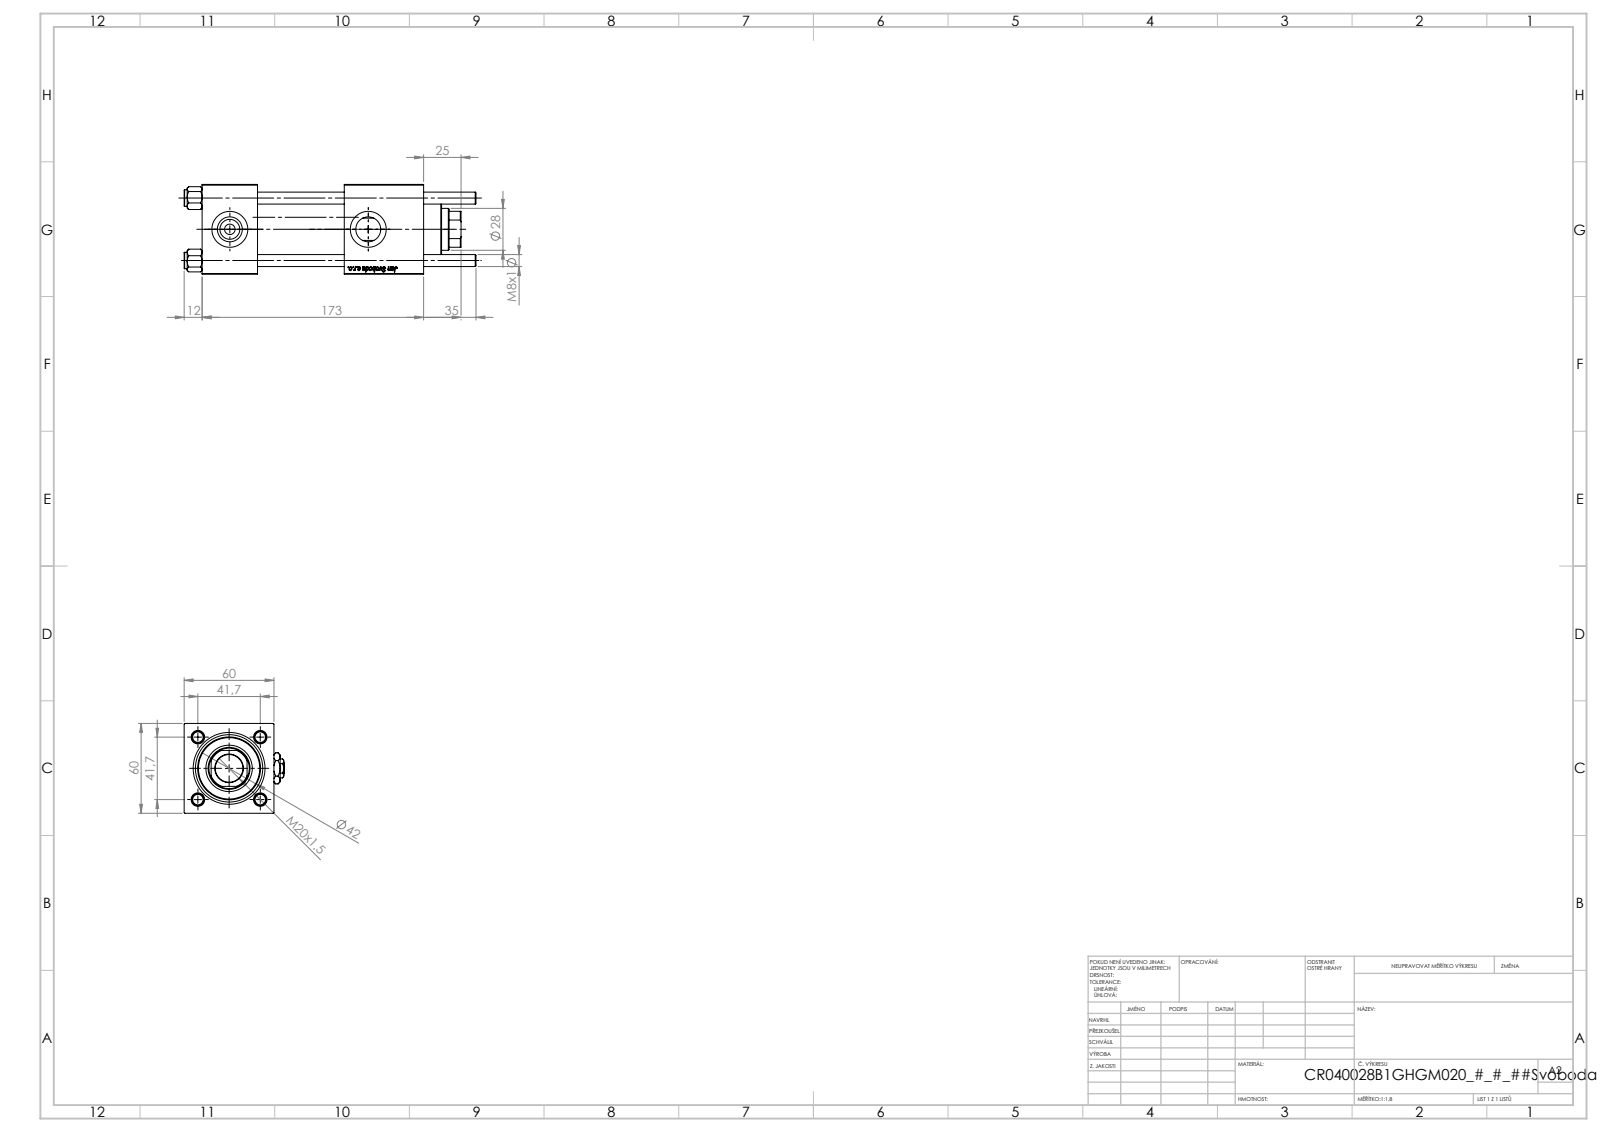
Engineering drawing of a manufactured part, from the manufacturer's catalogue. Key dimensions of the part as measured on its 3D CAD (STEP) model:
Part name (STEP PRODUCT): NUT_M5_B; Zatka_pro_OIL_PORT; V215CR_B-1; V215_VC_A (+2 more)
STEP written by: SolidWorks 2019 (CONFIG_CONTROL_DESIGN)
Units: millimetres
Bodies: 12 solids, 1207 faces (457 planar, 82 cylindrical, 668 other)
Overall size (bounding box): 195 × 67 × 60
Volume: 433 684 mm³ · Surface area: 121 123 mm²
Round holes (diameter × count): ⌀8 ×4, ⌀7 ×2, ⌀16.66 ×2, ⌀24 ×2, ⌀18.5 ×1, ⌀28 ×1, ⌀31 ×1, ⌀40 ×1, ⌀45 ×1
Round bosses / shafts (diameter × count): ⌀11 ×4, ⌀46 ×1, ⌀42 ×1
Partial cylindrical surfaces — rounded edges, fillets, slot ends (radius × count): R13.5 ×1
Main face-to-face distances: 60, 37, 58, 95, 53, 119.3, 82.3, 24.3, 148, 111
Hole centre spacings: 29.49, 41.7, 58.97, 92.5
